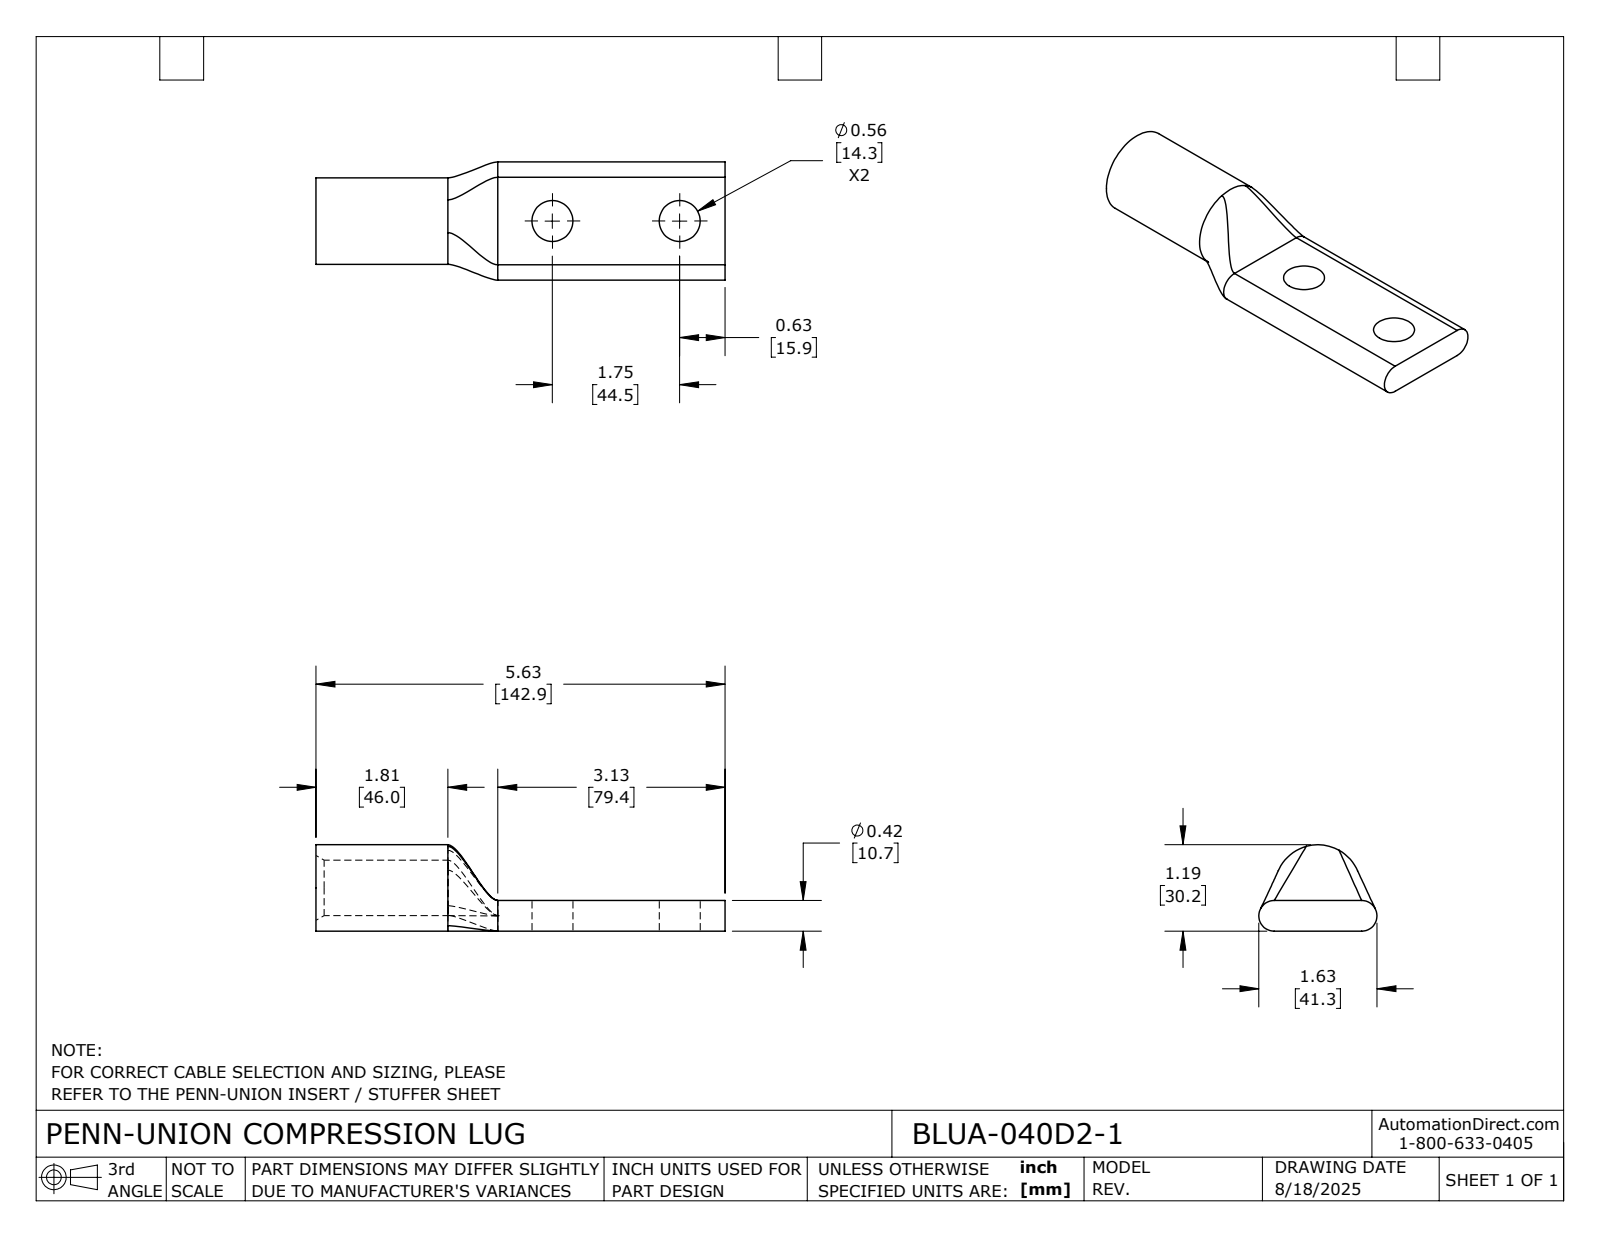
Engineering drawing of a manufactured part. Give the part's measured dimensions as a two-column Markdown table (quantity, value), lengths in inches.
| quantity | value |
| --- | --- |
| part name | BLUA-040D2-1 |
| STEP written by | SolidWorks 2024 (CONFIG_CONTROL_DESIGN) |
| units | inches |
| bodies | 1 solid, 26 faces (5 planar, 11 cylindrical, 10 other) |
| overall size | 5.625 × 1.625 × 1.188 |
| volume | 3.43 in³ |
| surface area | 29.35 in² |
| round holes (diameter × count) | 0.563 × 2, 0.762 × 1 |
| round bosses / shafts (diameter × count) | 1.188 × 1 |
| partial cylindrical surfaces (radius × count) | 0.211 × 2 |
| main face-to-face distances | 0.422, 5.625, 2.5, 3.125 |
| hole center spacings | 1.75 |
